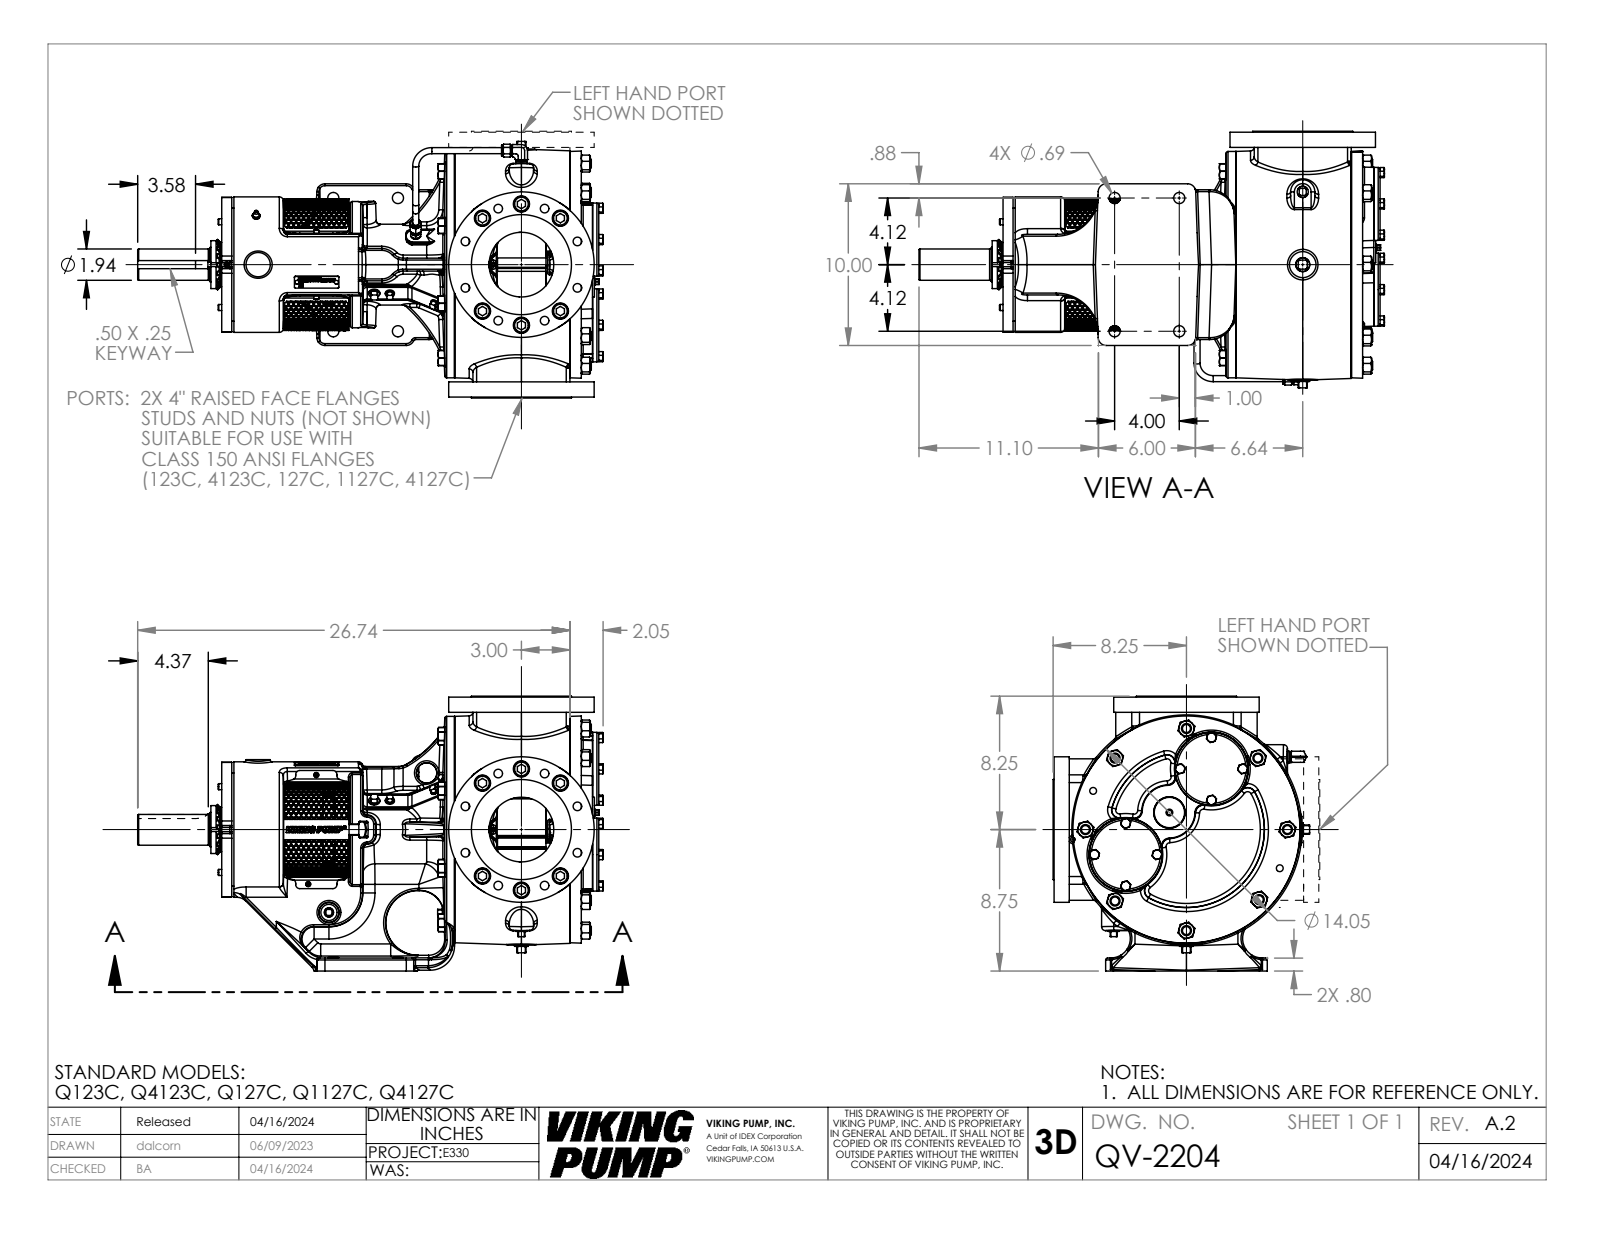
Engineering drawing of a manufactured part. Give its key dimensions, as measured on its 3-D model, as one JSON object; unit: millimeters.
{"part_name": "QV-2204", "step_written_by": "SolidWorks 2022 (AUTOMOTIVE_DESIGN)", "units": "millimeters", "bodies": {"solids": 1, "faces": 7404, "planar": 2715, "cylindrical": 641, "other": 4048}, "overall_size": [725.53, 431.8, 406.27], "volume_mm3": 32650000, "surface_area_mm2": 1286000, "round_holes": [[13.49, 16], [25.4, 12], [6.76, 8], [29.38, 8], [6.35, 6], [17.48, 4], [4.04, 2], [7.94, 2], [8.38, 2], [101.6, 2], [5.41, 1], [11.51, 1]], "round_bosses_or_shafts": [[23.81, 12], [15.68, 8], [11.11, 3], [7.92, 3], [228.6, 2], [157.23, 2], [9.53, 2], [355.6, 1]], "partial_cylinders_radius": [[3.05, 60], [6.35, 29], [0.38, 18], [2.34, 18], [12.7, 16], [19.05, 16], [0.76, 12], [6.1, 8]], "face_to_face_distances": [23.88, 95.25, 1.52, 25.4, 565.3, 430.28, 470.05, 406.4, 527.2, 431.95], "hole_center_spacings": [95.25, 134.7, 72.9, 176, 52.39, 190.5, 37.16, 68.99]}
